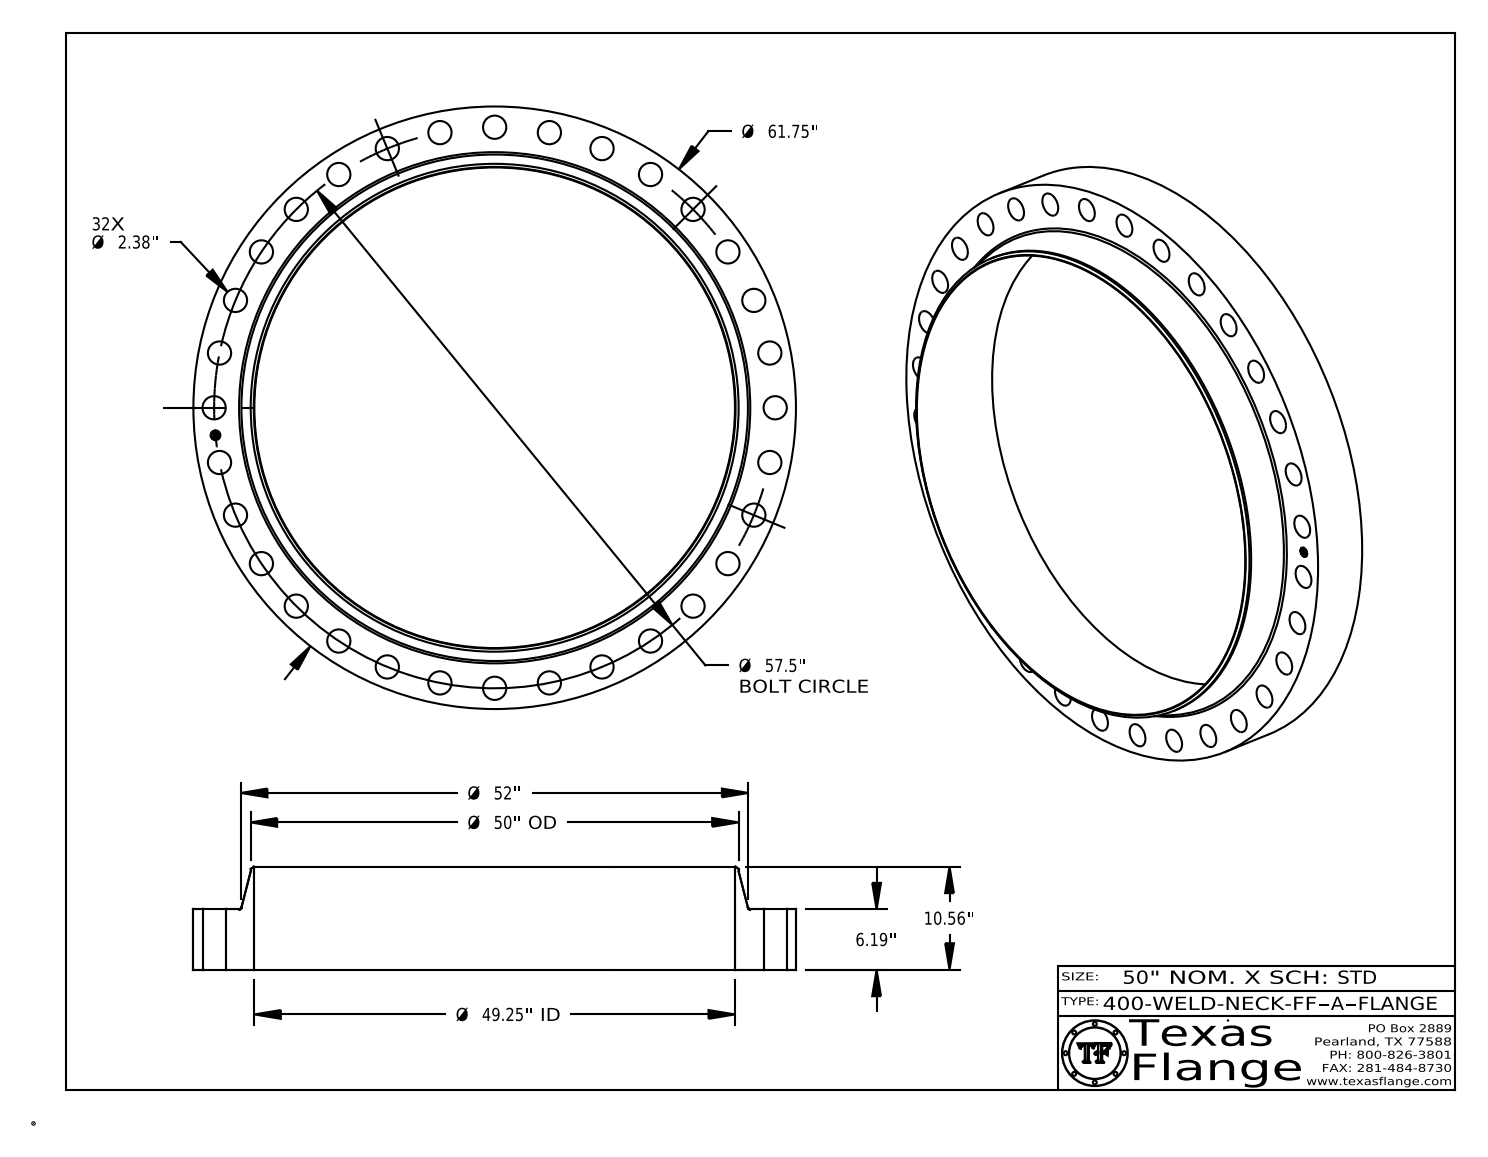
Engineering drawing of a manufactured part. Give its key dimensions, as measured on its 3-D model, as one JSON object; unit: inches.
{"part_name": "400-WELD-NECK-FF, Series A", "step_written_by": "CATIA V5 STEP AP214 (AUTOMOTIVE_DESIGN)", "units": "inches", "bodies": {"solids": 1, "faces": 464, "planar": 368, "cylindrical": 90, "other": 6}, "overall_size": [61.75, 61.75, 10.56], "volume_in3": 6425, "surface_area_in2": 6735, "round_holes": [[2.38, 32], [1, 1], [49.25, 1]], "round_bosses_or_shafts": [[0.061, 8], [61.75, 1], [50, 1], [0.788, 1]], "face_to_face_distances": [6.19, 10.56, 4.37, 0.015, 6.175, 4.385, 0.298, 0.292, 0.054, 0.193], "hole_center_spacings": [44.448, 28.75, 22.004, 57.223, 27.105, 50.71, 55.024, 5.636]}
